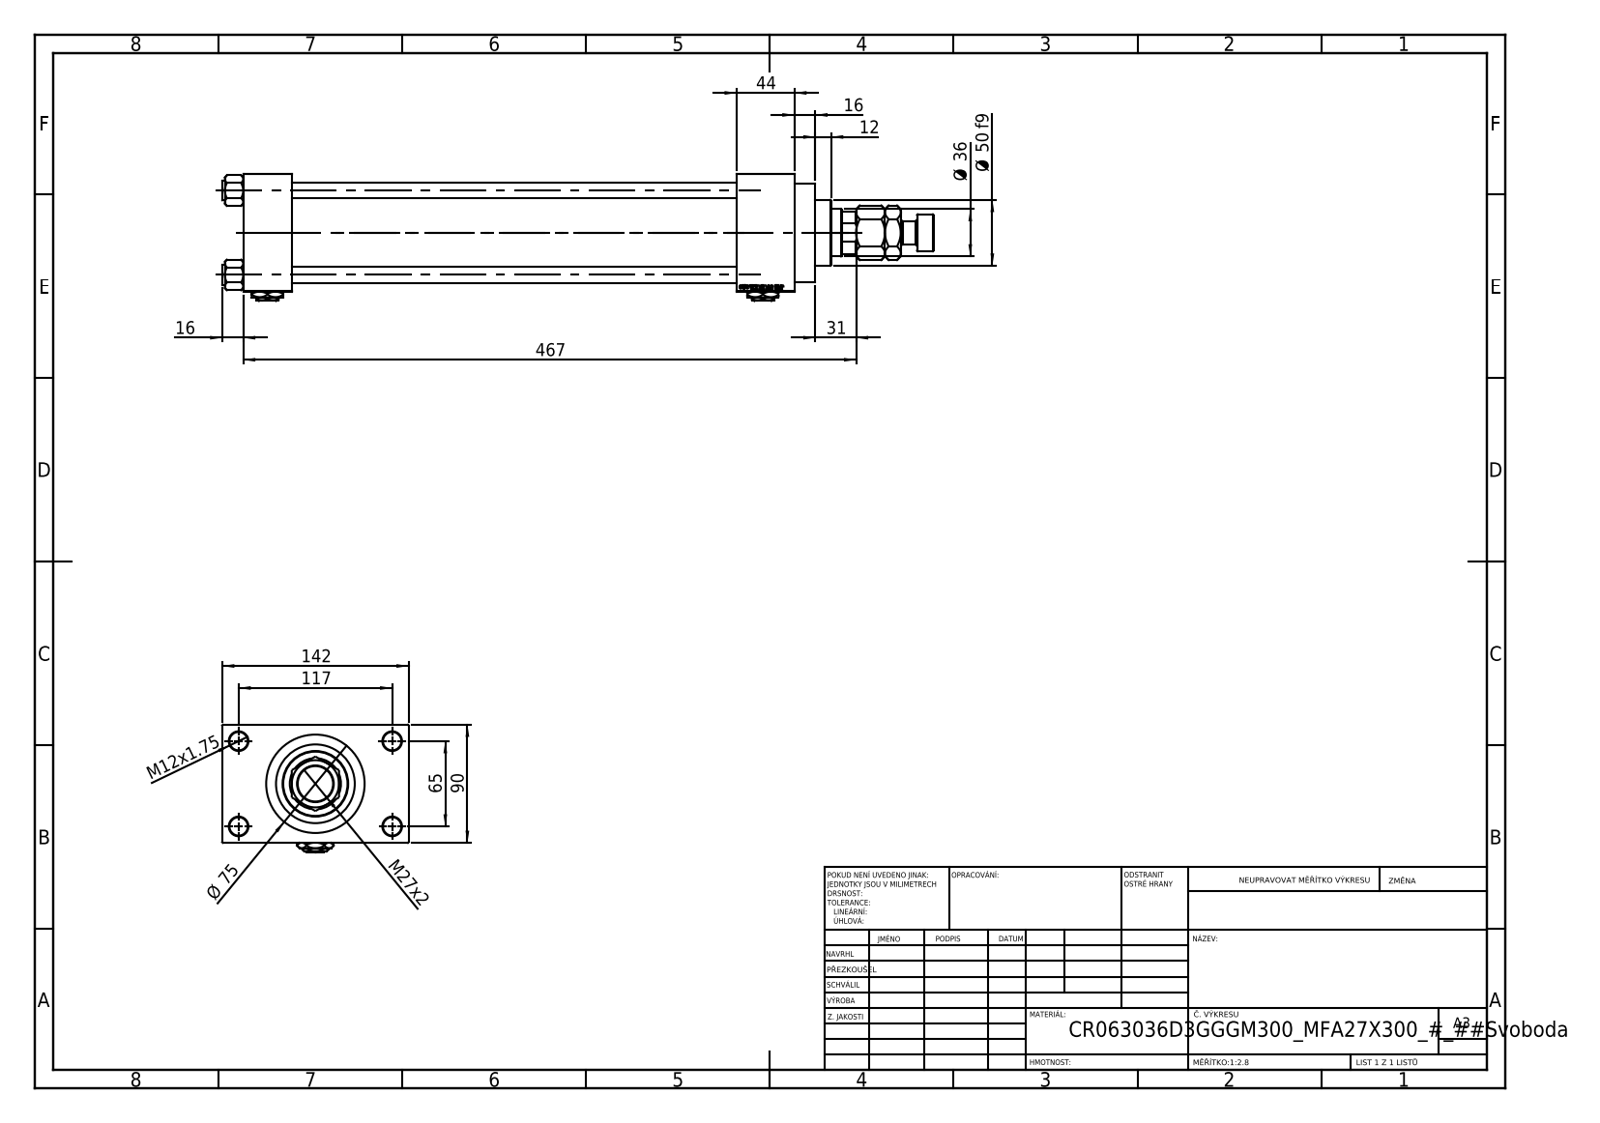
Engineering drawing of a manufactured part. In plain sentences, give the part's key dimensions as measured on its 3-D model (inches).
The part is named "NUT_M5_D; V215CR_D_TYCINKA; V215_VC_A; V215CR_VCP_D (+3 more)". Its 3-D file was written by "SolidWorks 2019 (CONFIG_CONTROL_DESIGN)". It is 14 solids with 1257 faces: 561 planar, 104 cylindrical and 592 other. Overall it measures 21.339 by 5.591 by 3.819 inches. Its volume is 106.7 cubic inches and its surface area 631.6 square inches. Round holes: 4 of diameter 0.472, 4 of diameter 0.551, 2 of diameter 0.276, 2 of diameter 0.825, 2 of diameter 1.181, 1 of diameter 1.004, 1 of diameter 1.417, 1 of diameter 1.535, 1 of diameter 1.969, 1 of diameter 2.362, 1 of diameter 2.48. Round bosses or shafts: 4 of diameter 0.591, 1 of diameter 2.953, 1 of diameter 2.717, 1 of diameter 1.102, 1 of diameter 0.709. Partial cylindrical surfaces (rounded edges, fillets, slot ends): 1 of radius 0.689. The main face-to-face distances are 3.543, 13.346, 1.457, 14.803, 16.535, 15.079, 1.732, 1.024, 4.567, 5.591. The hole center spacings are 1.037, 1.79, 2.531, 2.635, 2.748, 3.569, 4.383, 2.559.
